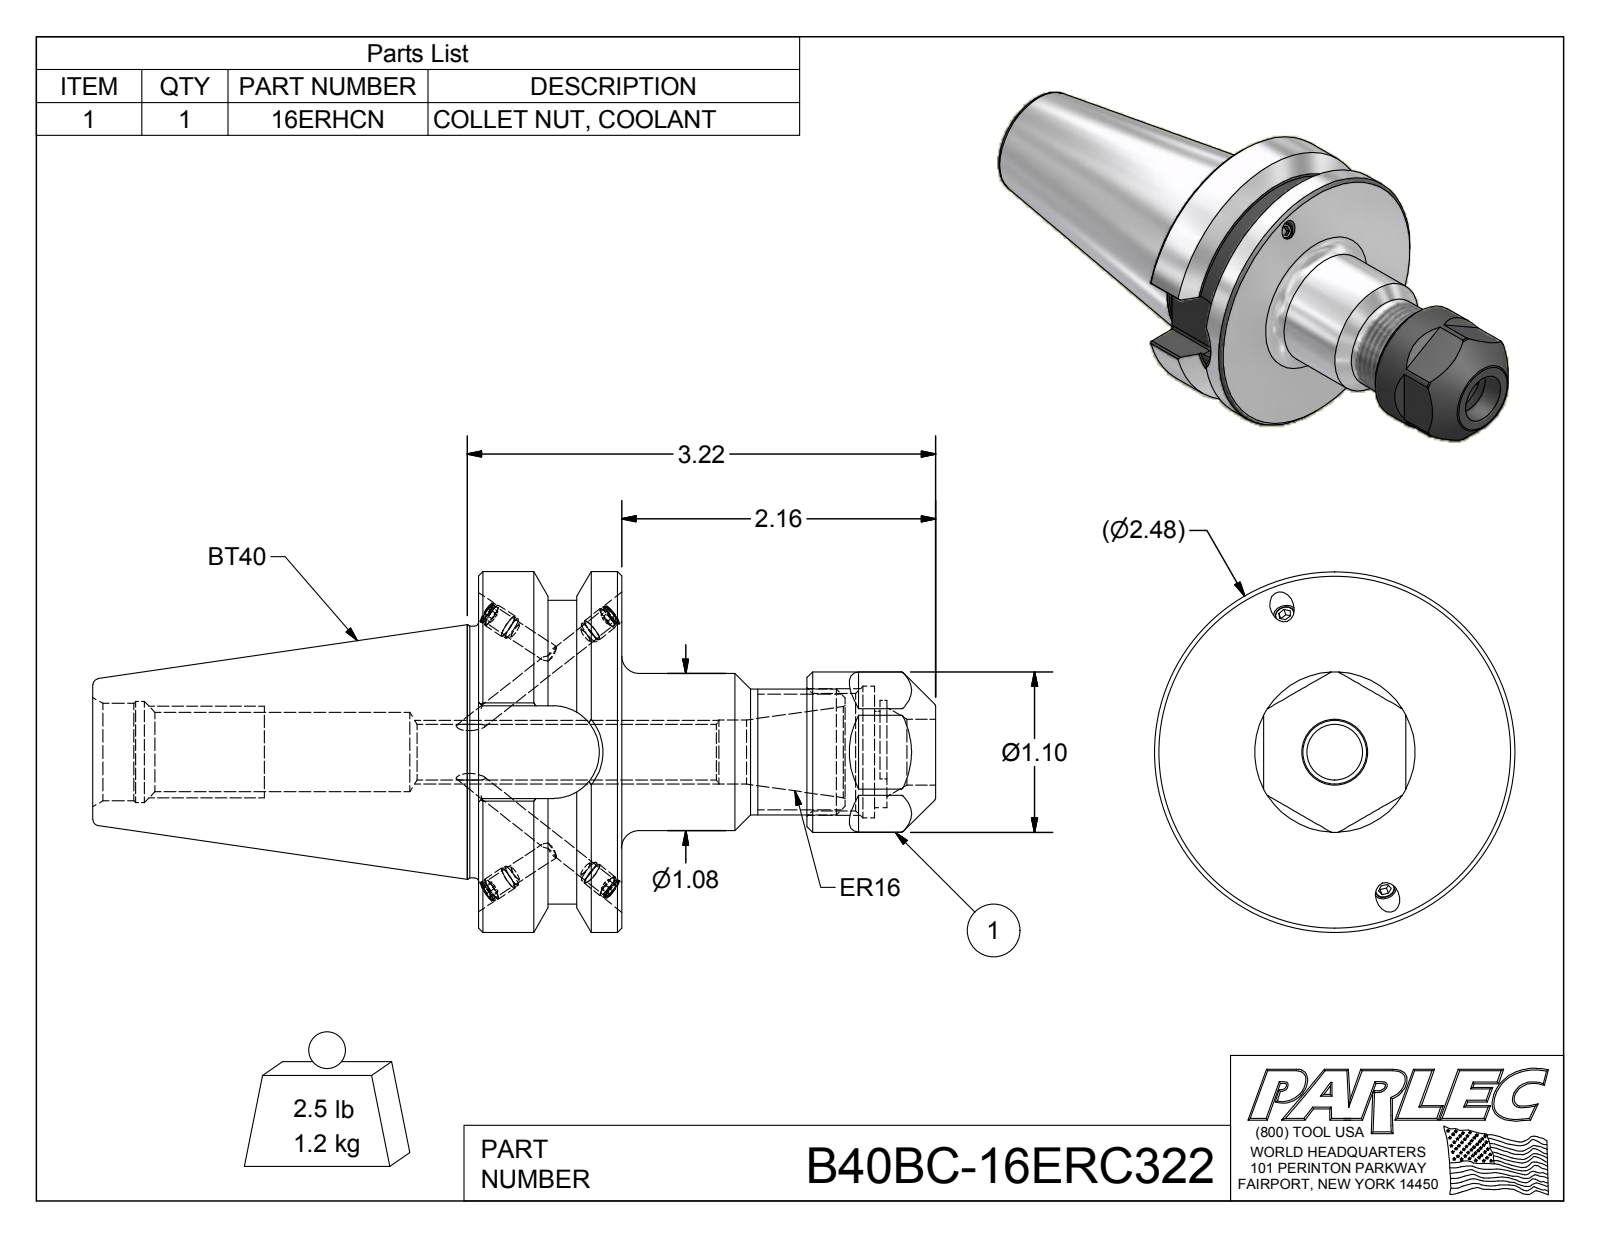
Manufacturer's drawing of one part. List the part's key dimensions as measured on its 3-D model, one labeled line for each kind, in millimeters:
Part name (STEP PRODUCT): B40BC-16ERC322; B40BCB-16ER3-1; 029-965; 16ERHCN
STEP written by: Autodesk Inventor 2012 (AUTOMOTIVE_DESIGN)
Units: millimetres
Bodies: 6 solids, 186 faces (84 planar, 49 cylindrical, 53 other)
Overall size (bounding box): 147.2 × 63 × 63
Volume: 142 700 mm³ · Surface area: 31 320 mm²
Round holes (diameter × count): ⌀3.3 ×4, ⌀4.1 ×4, ⌀9.7 ×1, ⌀11.2 ×1, ⌀11.5 ×1, ⌀13.8 ×1, ⌀16.8 ×1, ⌀17 ×1, ⌀17.6 ×1, ⌀20.5 ×1, ⌀23 ×1
Round bosses / shafts (diameter × count): ⌀4.2 ×4, ⌀4 ×4, ⌀63 ×1, ⌀53 ×1, ⌀43.9 ×1, ⌀28 ×1, ⌀27.4 ×1, ⌀22 ×1
Partial cylindrical surfaces — rounded edges, fillets, slot ends (radius × count): R0.5 ×8, R8.1 ×1, R9 ×1
Main face-to-face distances: 25, 24.9, 45.2, 10.2, 35.1, 69.1, 44.1, 67.4, 92.4, 136.5
Hole centre spacings: 1.3
